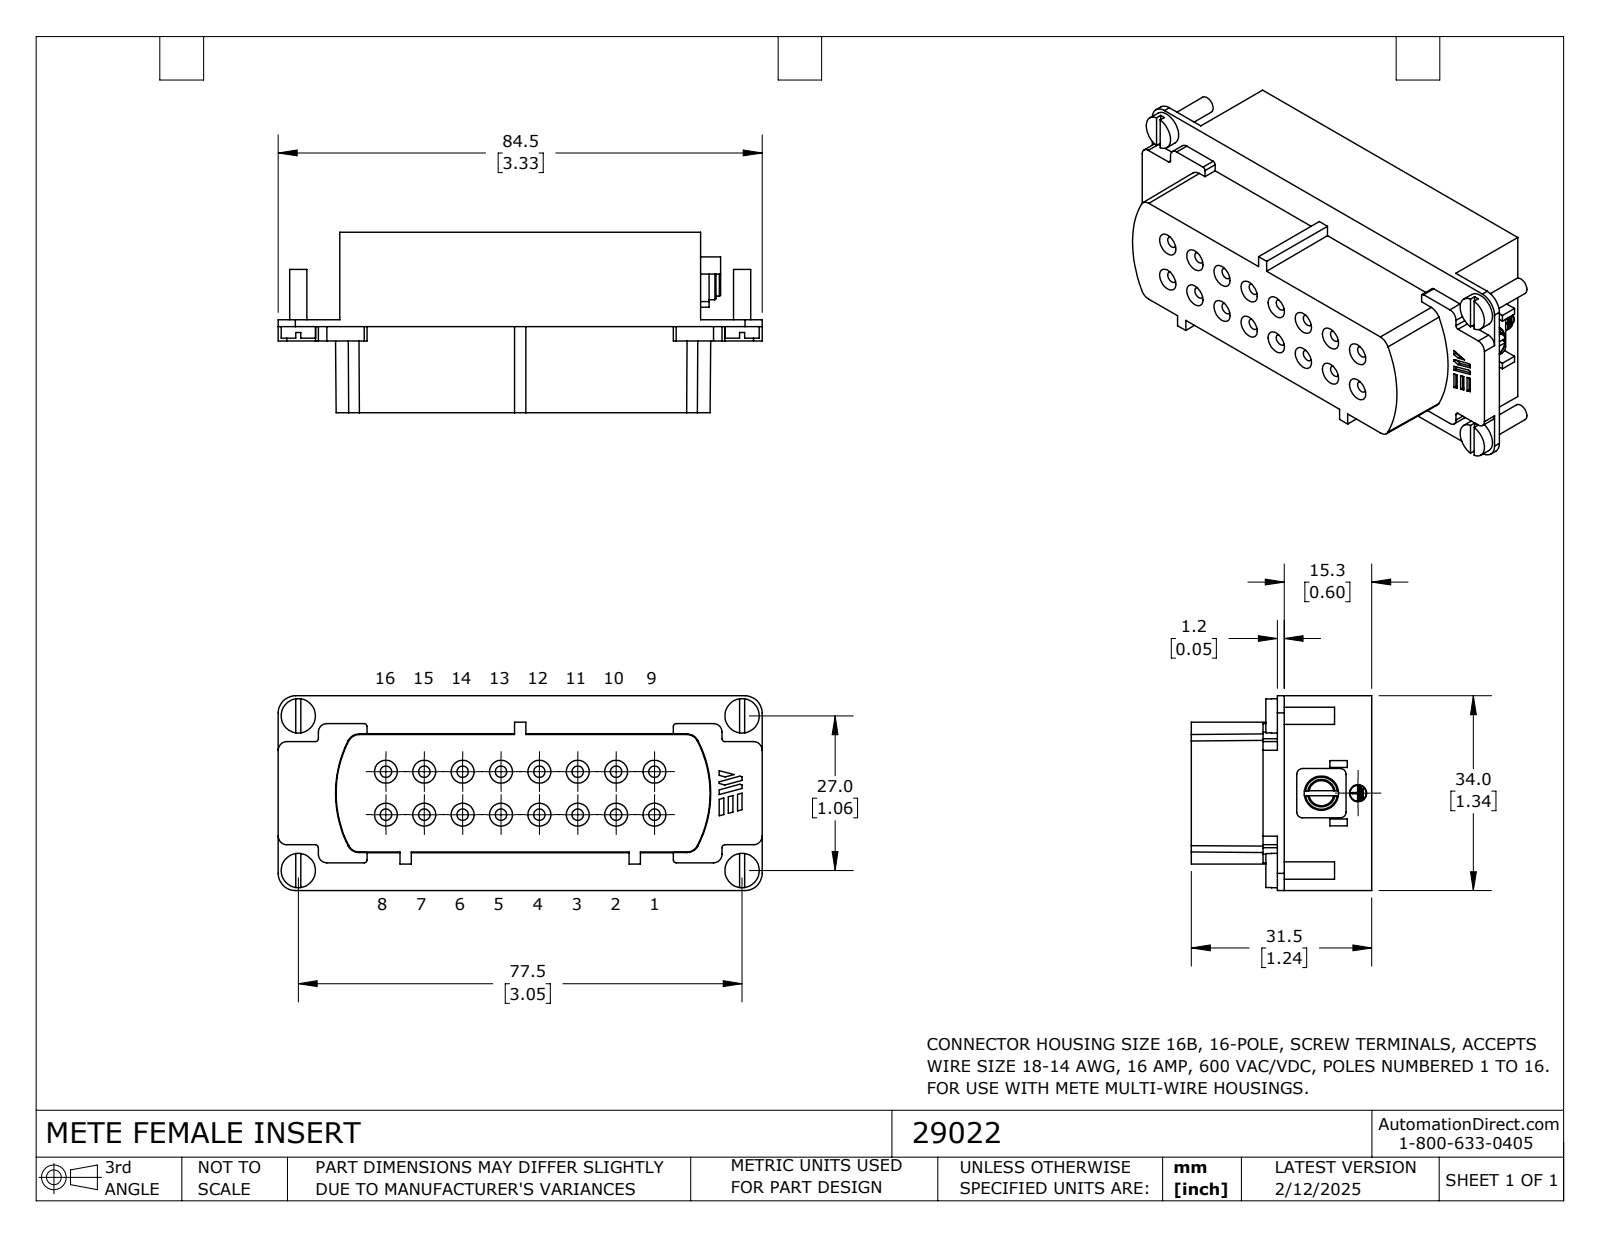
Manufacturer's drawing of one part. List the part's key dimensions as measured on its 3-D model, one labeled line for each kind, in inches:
Part name (STEP PRODUCT): 29022
STEP written by: SolidWorks 2024 (CONFIG_CONTROL_DESIGN)
Units: inches
Bodies: 1 solid, 266 faces (144 planar, 80 cylindrical, 42 other)
Overall size (bounding box): 3.327 × 1.339 × 1.24
Volume: 3.427 in³ · Surface area: 23.94 in²
Round holes (diameter × count): ⌀0.079 ×16, ⌀0.118 ×1
Round bosses / shafts (diameter × count): ⌀0.236 ×5, ⌀0.118 ×4, ⌀0.189 ×1, ⌀0.11 ×1
Partial cylindrical surfaces — rounded edges, fillets, slot ends (radius × count): R0.02 ×8, R0.059 ×8, R0.039 ×4, R0.118 ×4
Main face-to-face distances: 1.24, 1.339, 0.591, 0.65, 0.047, 0.638, 0.602, 0.492, 0.098, 2.48
Hole centre spacings: 0.264, 0.396, 0.528, 0.605, 0.791, 0.844, 0.295, 1.055
